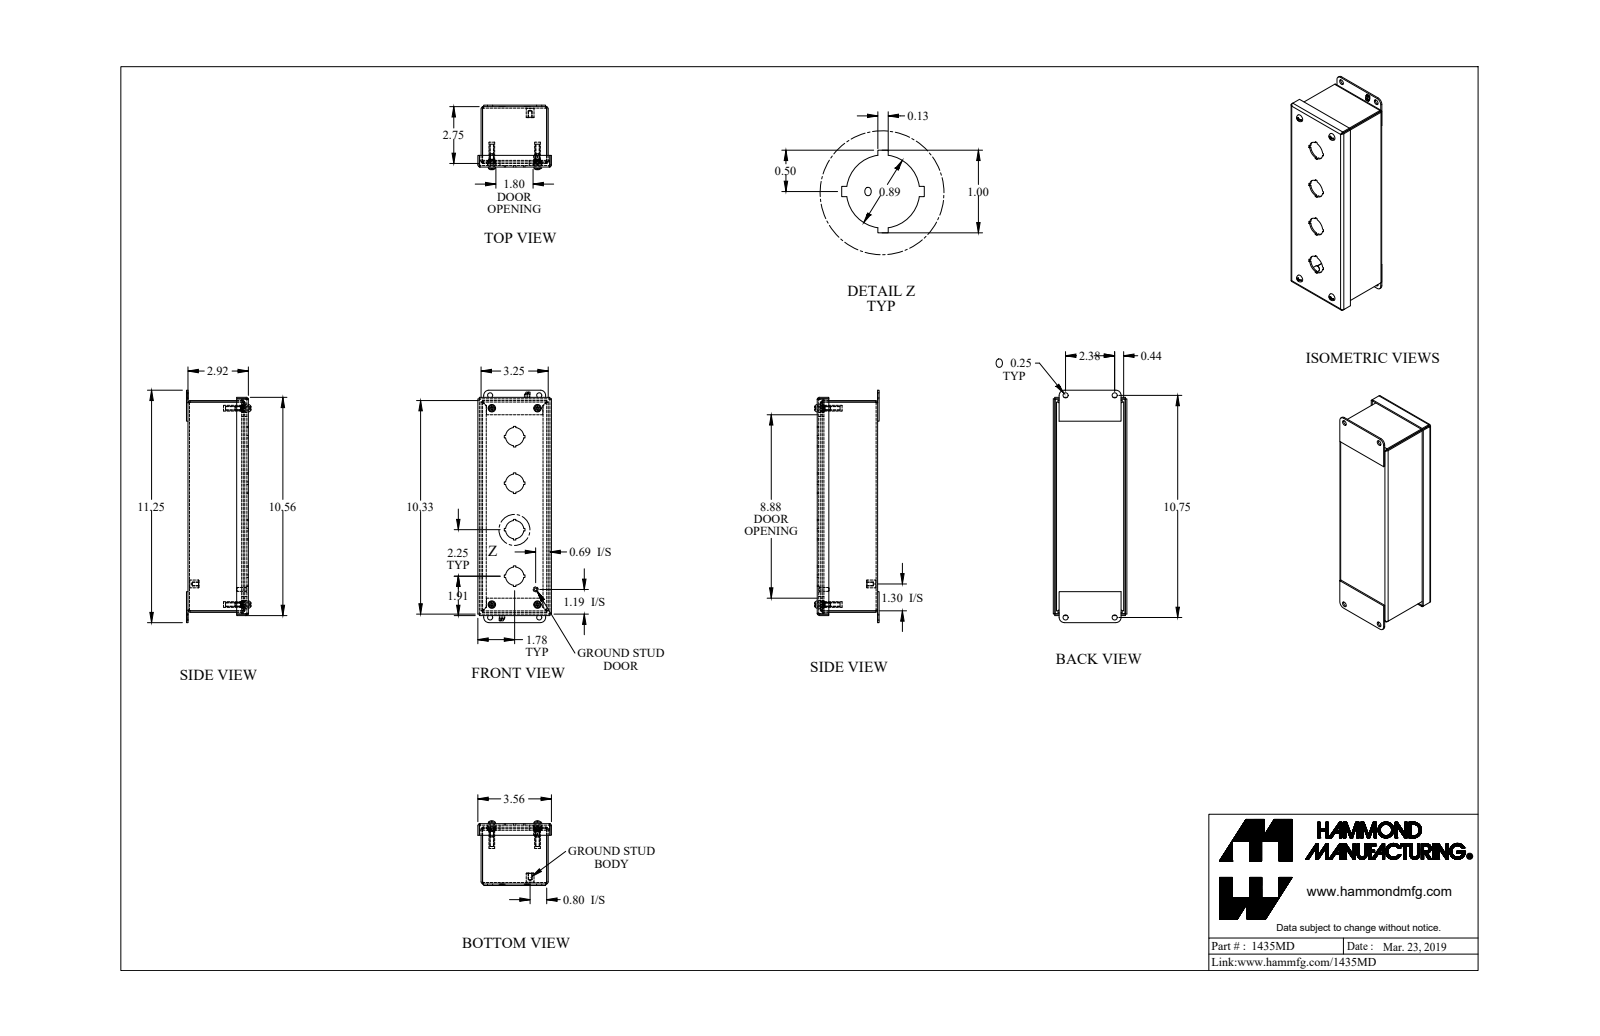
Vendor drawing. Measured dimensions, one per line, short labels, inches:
name: 1435MD_Default
written by: SolidWorks 2019 (CONFIG_CONTROL_DESIGN)
unit: in
bodies: 19 solids, 619 faces (407 planar, 156 cylindrical, 56 other)
size: 11.25 × 3.562 × 3.121
volume: 14.81 in³; area: 385.9 in²
holes: 8× ⌀0.25, 4× ⌀0.159, 4× ⌀0.406, 4× ⌀0.886, 1× ⌀0.156
bosses: 4× ⌀0.39, 4× ⌀0.275, 4× ⌀0.19, 4× ⌀0.148, 1× ⌀0.375, 1× ⌀0.25, 1× ⌀0.188
rounds: 12× R0.036, 12× R0.108, 4× R0.16, 4× R0.171, 4× R0.25
face distances: 0.072, 2.85, 0.072, 3.178, 2.922, 2.778, 3.25, 3.106, 10.178, 0.156
hole spacings: 9.5, 10.126, 10.381, 9.754, 2.376, 0.63, 0.631, 1.765
